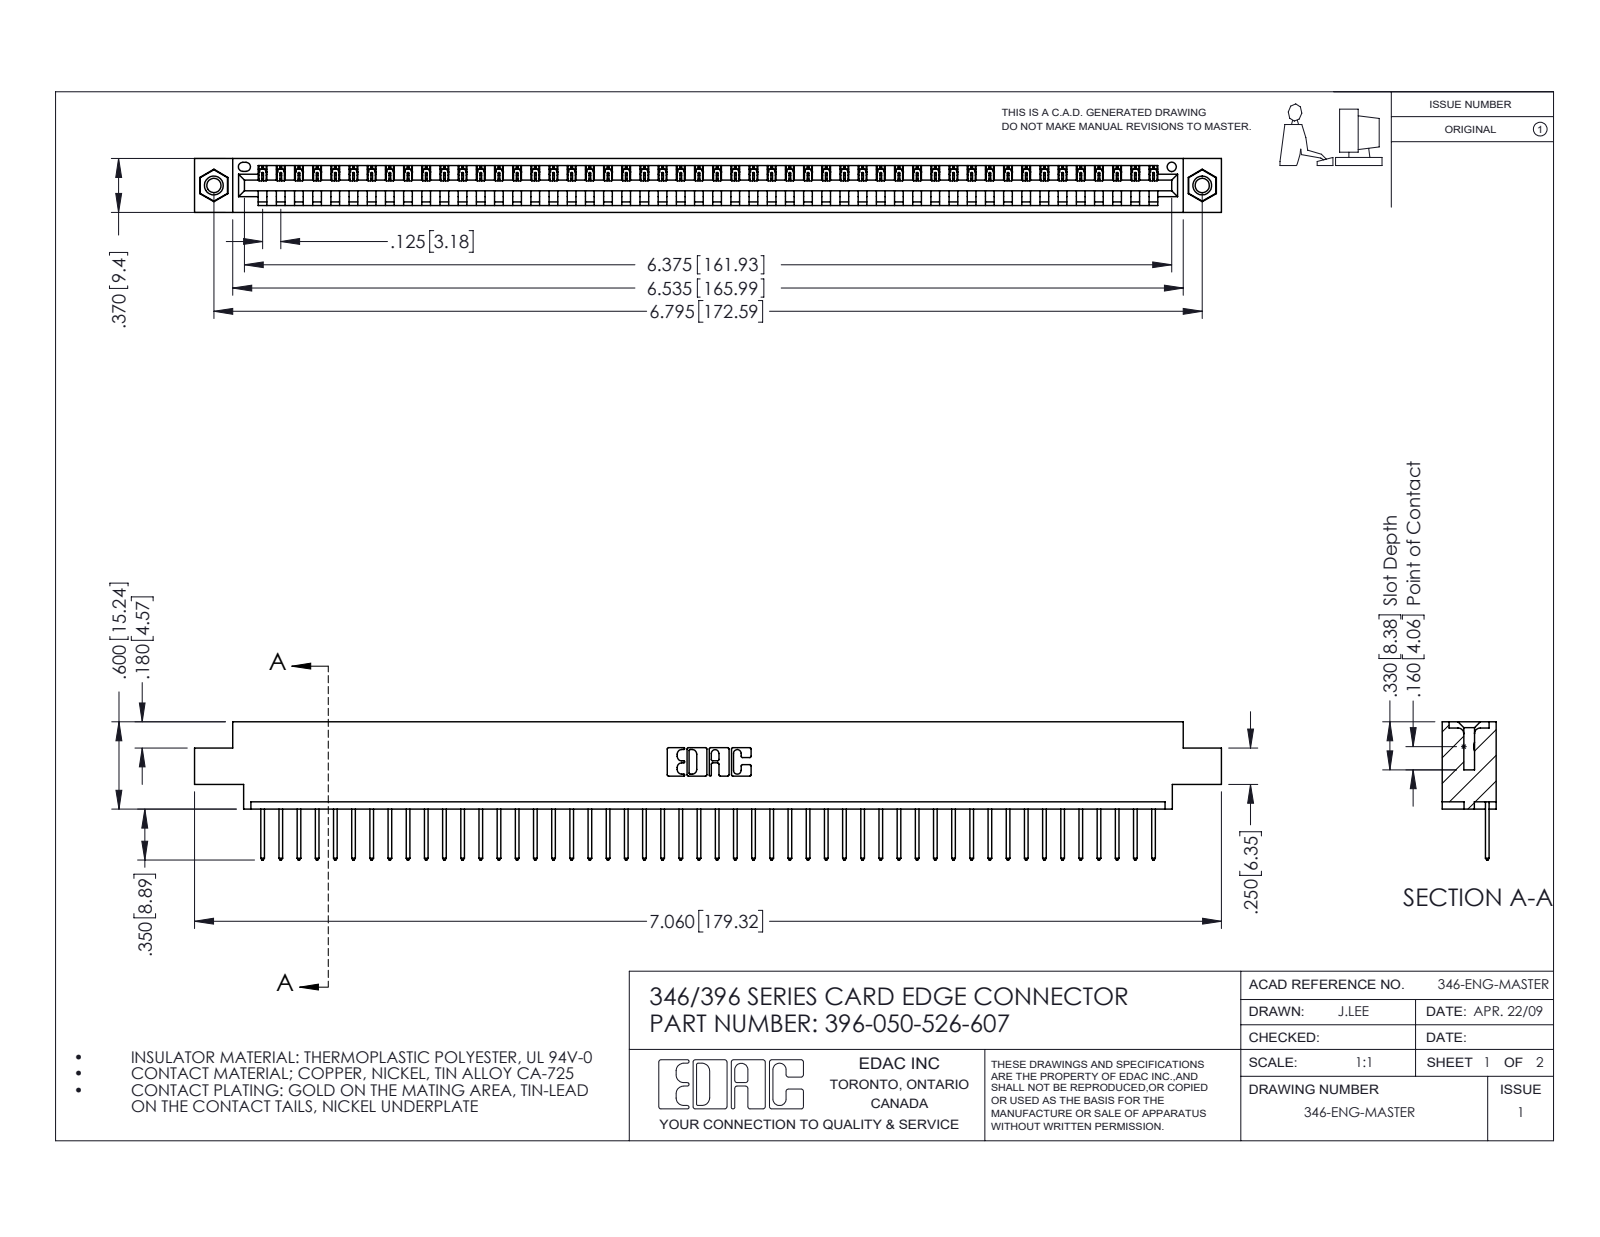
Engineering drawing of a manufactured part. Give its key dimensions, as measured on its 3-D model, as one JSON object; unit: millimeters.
{"part_name": "346 Part_0.170 Offset - 0.156 Dia-TI; 345-292-001_345-293-126; 396-050-526-607; 345-250-001_345-250-005-103", "step_written_by": "SolidWorks 2016 (CONFIG_CONTROL_DESIGN)", "units": "millimeters", "bodies": {"solids": 53, "faces": 3086, "planar": 2112, "cylindrical": 958, "other": 16}, "overall_size": [179.3, 24.1, 9.4], "volume_mm3": 17010, "surface_area_mm2": 21500, "round_holes": [[2.5, 2], [3.2, 2], [4, 2], [1.6, 1]], "round_bosses_or_shafts": [[3.9, 2]], "partial_cylinders_radius": [[0.2, 100], [0.3, 100], [0.3, 22], [0.2, 6], [0.8, 6], [0.7, 3], [0.8, 2], [1, 2]], "face_to_face_distances": [1.2, 8.2, 9.4, 6.4, 1.8, 7.6, 0.6, 5.6, 3.8, 2.5], "hole_center_spacings": [6.2, 167.3, 172.6]}
